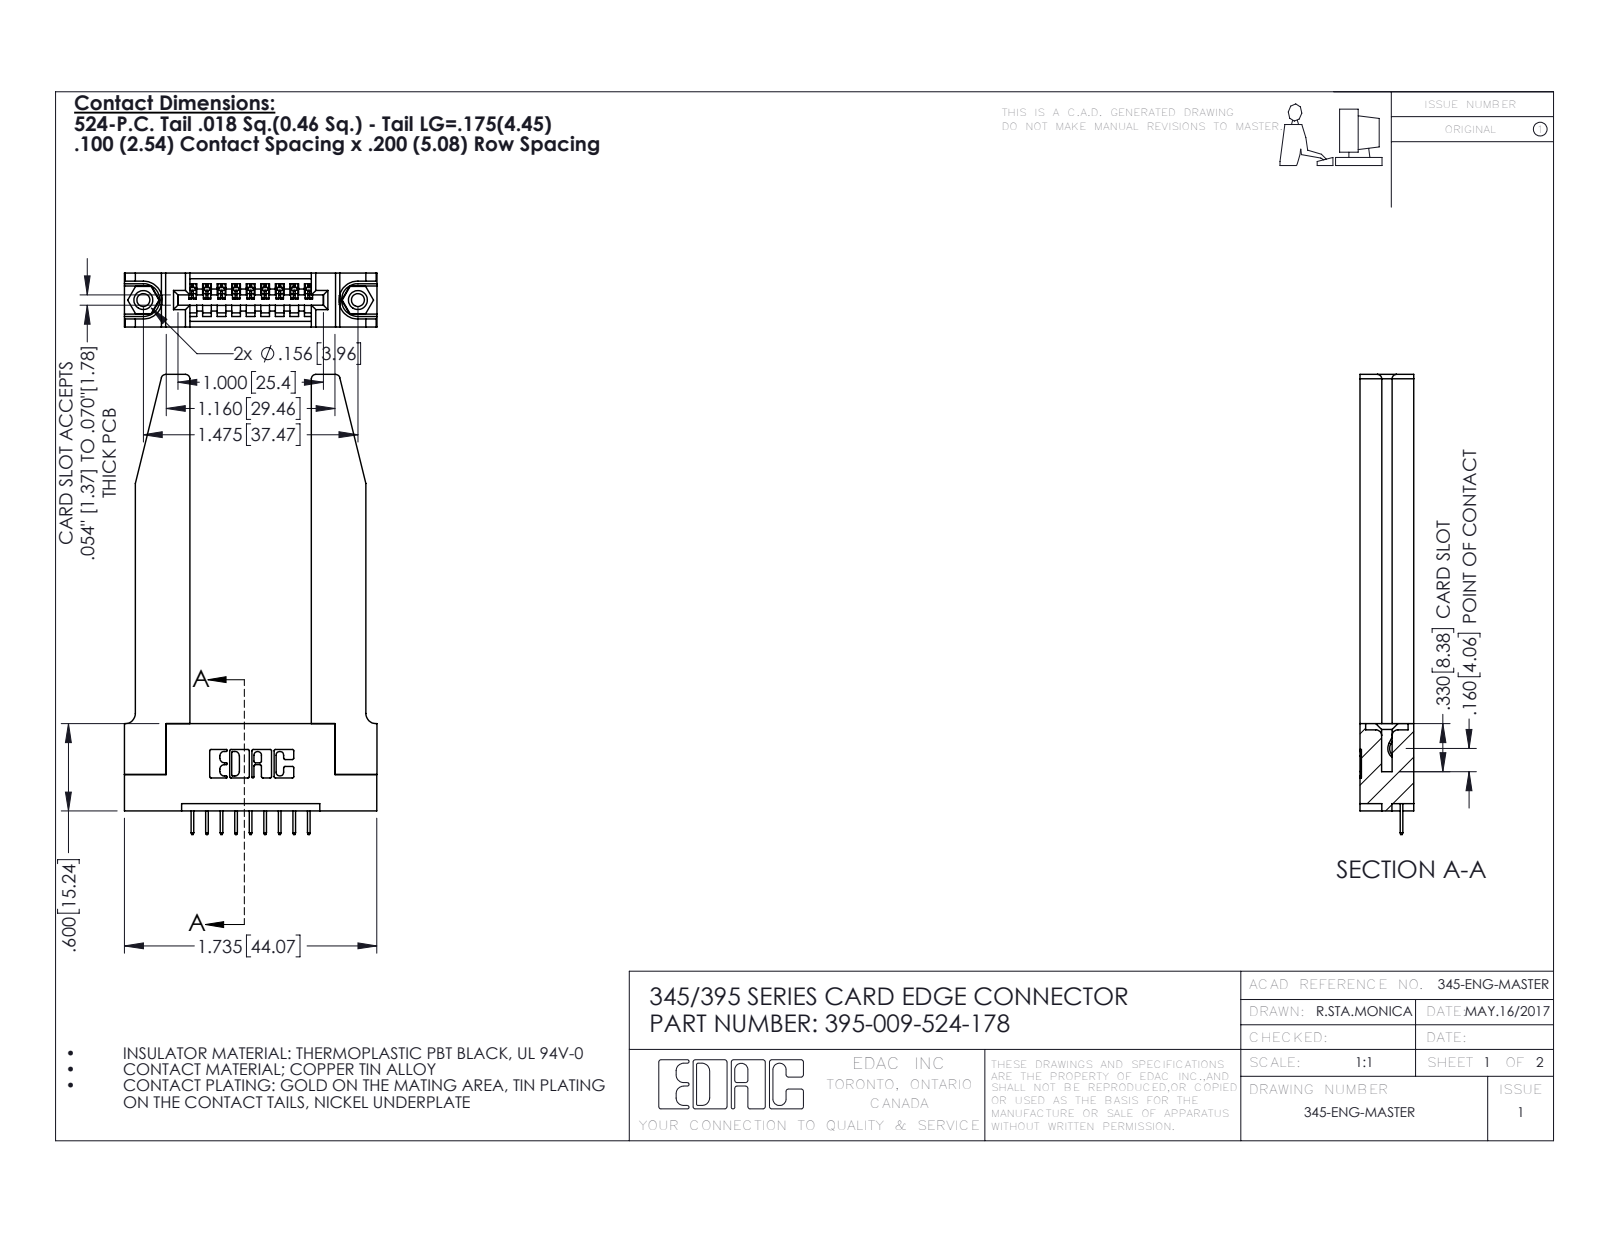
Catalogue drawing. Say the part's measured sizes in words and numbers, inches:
The part is named "345-292-001_345-293-124; 345 Part_Flush Mounting Lugs - 0.156 Dia-TH; 395-009-524-178; 345-220-078_345-220-078 (+1 more)". Its 3-D file was written by "SolidWorks 2016 (CONFIG_CONTROL_DESIGN)". It is 14 solids with 918 faces: 636 planar, 230 cylindrical and 52 other. Overall it measures 3.162 by 1.736 by 0.37 inches. Its volume is 0.711 cubic inches and its surface area 17.74 square inches. Round holes: 2 of diameter 0.089, 2 of diameter 0.125, 2 of diameter 0.156, 1 of diameter 0.064. Round bosses or shafts: 2 of diameter 0.155. Partial cylindrical surfaces (rounded edges, fillets, slot ends): 22 of radius 0.01, 18 of radius 0.006, 8 of radius 0.03, 6 of radius 0.007, 6 of radius 0.031, 3 of radius 0.026, 2 of radius 0.031, 2 of radius 0.04. The main face-to-face distances are 0.37, 0.15, 0.072, 0.148, 0.22, 0.298, 0.077, 0.835, 0.2, 0.095. The hole center spacings are 0.27, 1.244, 1.475.
